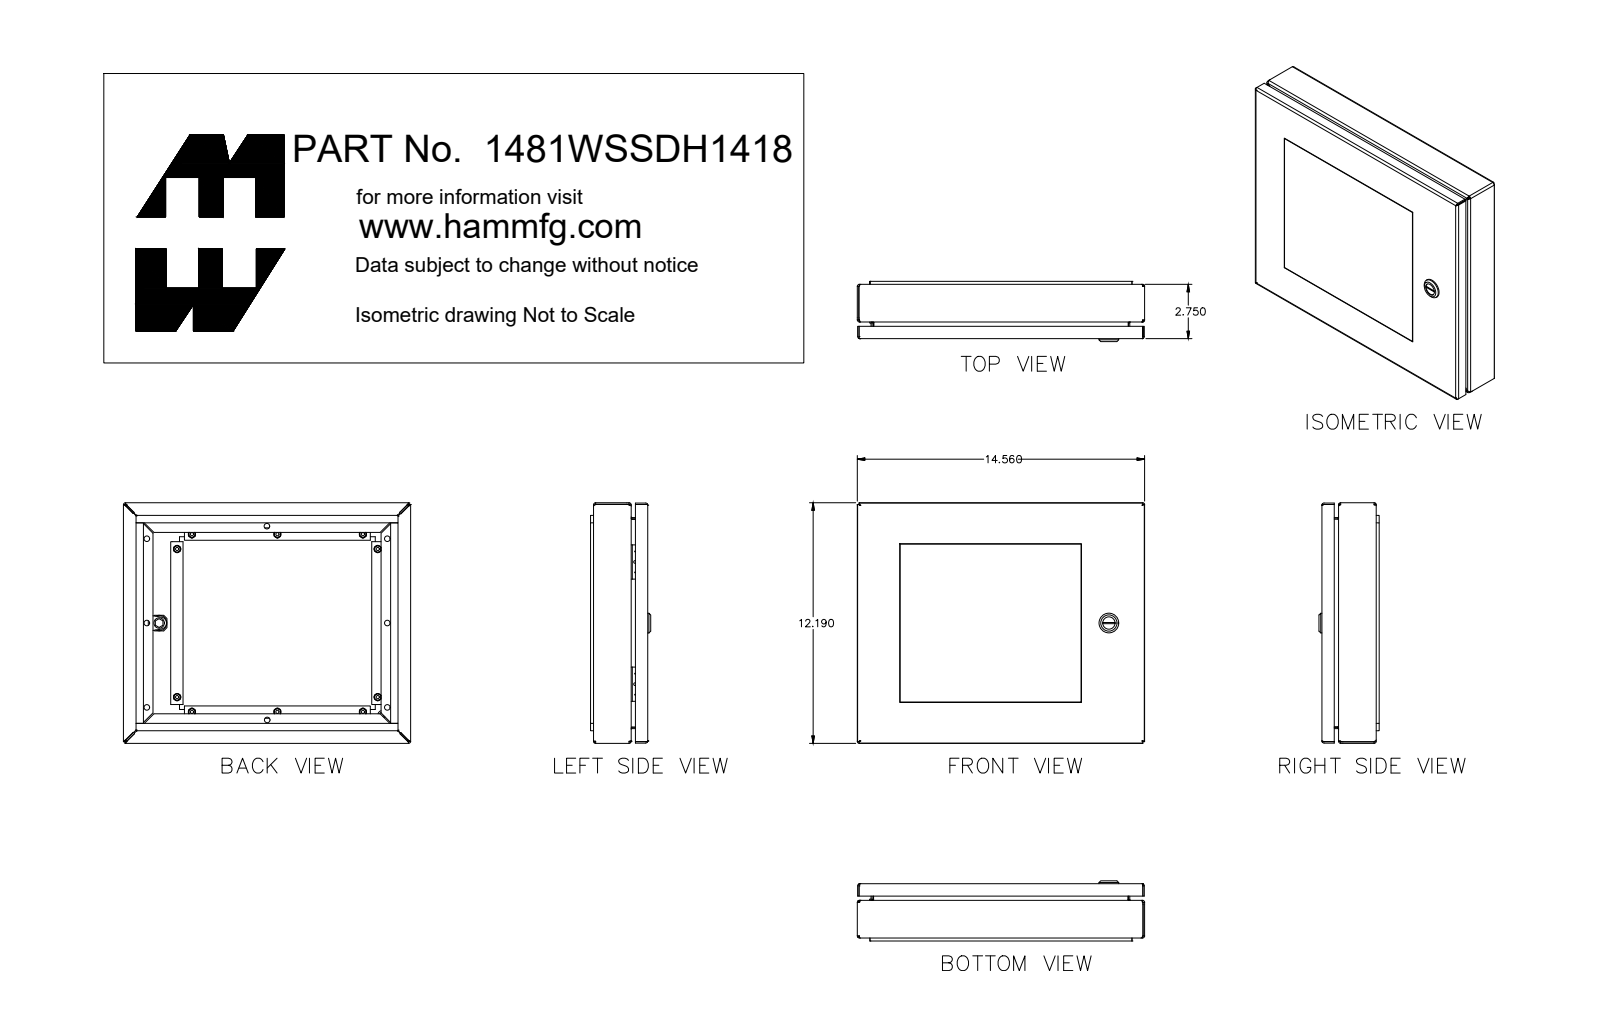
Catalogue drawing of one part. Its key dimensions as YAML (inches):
part_name: "1481WSSDH1418_Default"
step_written_by: "SolidWorks 2019 (CONFIG_CONTROL_DESIGN)"
units: inches
bodies: {solids: 42, faces: 999, planar: 541, cylindrical: 282, other: 176}
overall_size: [14.56, 12.19, 2.91]
volume: 49.41
surface_area: 1028
round_holes:
  - {diameter: 0.13, count: 10}
  - {diameter: 0.281, count: 8}
  - {diameter: 0.136, count: 2}
  - {diameter: 0.197, count: 1}
  - {diameter: 0.24, count: 1}
  - {diameter: 0.242, count: 1}
  - {diameter: 0.387, count: 1}
  - {diameter: 0.5, count: 1}
  - {diameter: 0.63, count: 1}
  - {diameter: 0.768, count: 1}
round_bosses_or_shafts:
  - {diameter: 0.368, count: 10}
  - {diameter: 0.226, count: 10}
  - {diameter: 0.164, count: 10}
  - {diameter: 1.1, count: 1}
  - {diameter: 0.785, count: 1}
  - {diameter: 0.625, count: 1}
  - {diameter: 0.525, count: 1}
  - {diameter: 0.477, count: 1}
partial_cylinders:
  - {radius: 0.036, count: 28}
  - {radius: 0.108, count: 28}
  - {radius: 0.101, count: 20}
  - {radius: 0.016, count: 4}
  - {radius: 0.088, count: 4}
  - {radius: 0.125, count: 2}
  - {radius: 0.021, count: 1}
  - {radius: 0.029, count: 1}
face_to_face_distances: [0.072, 0.25, 0.178, 2.578, 0.842, 1.736, 2.328, 0.592, 12.118, 14.488]
hole_center_spacings: [4.335, 6.125, 7.822, 9.45, 9.99, 11.017, 12.912, 9]
